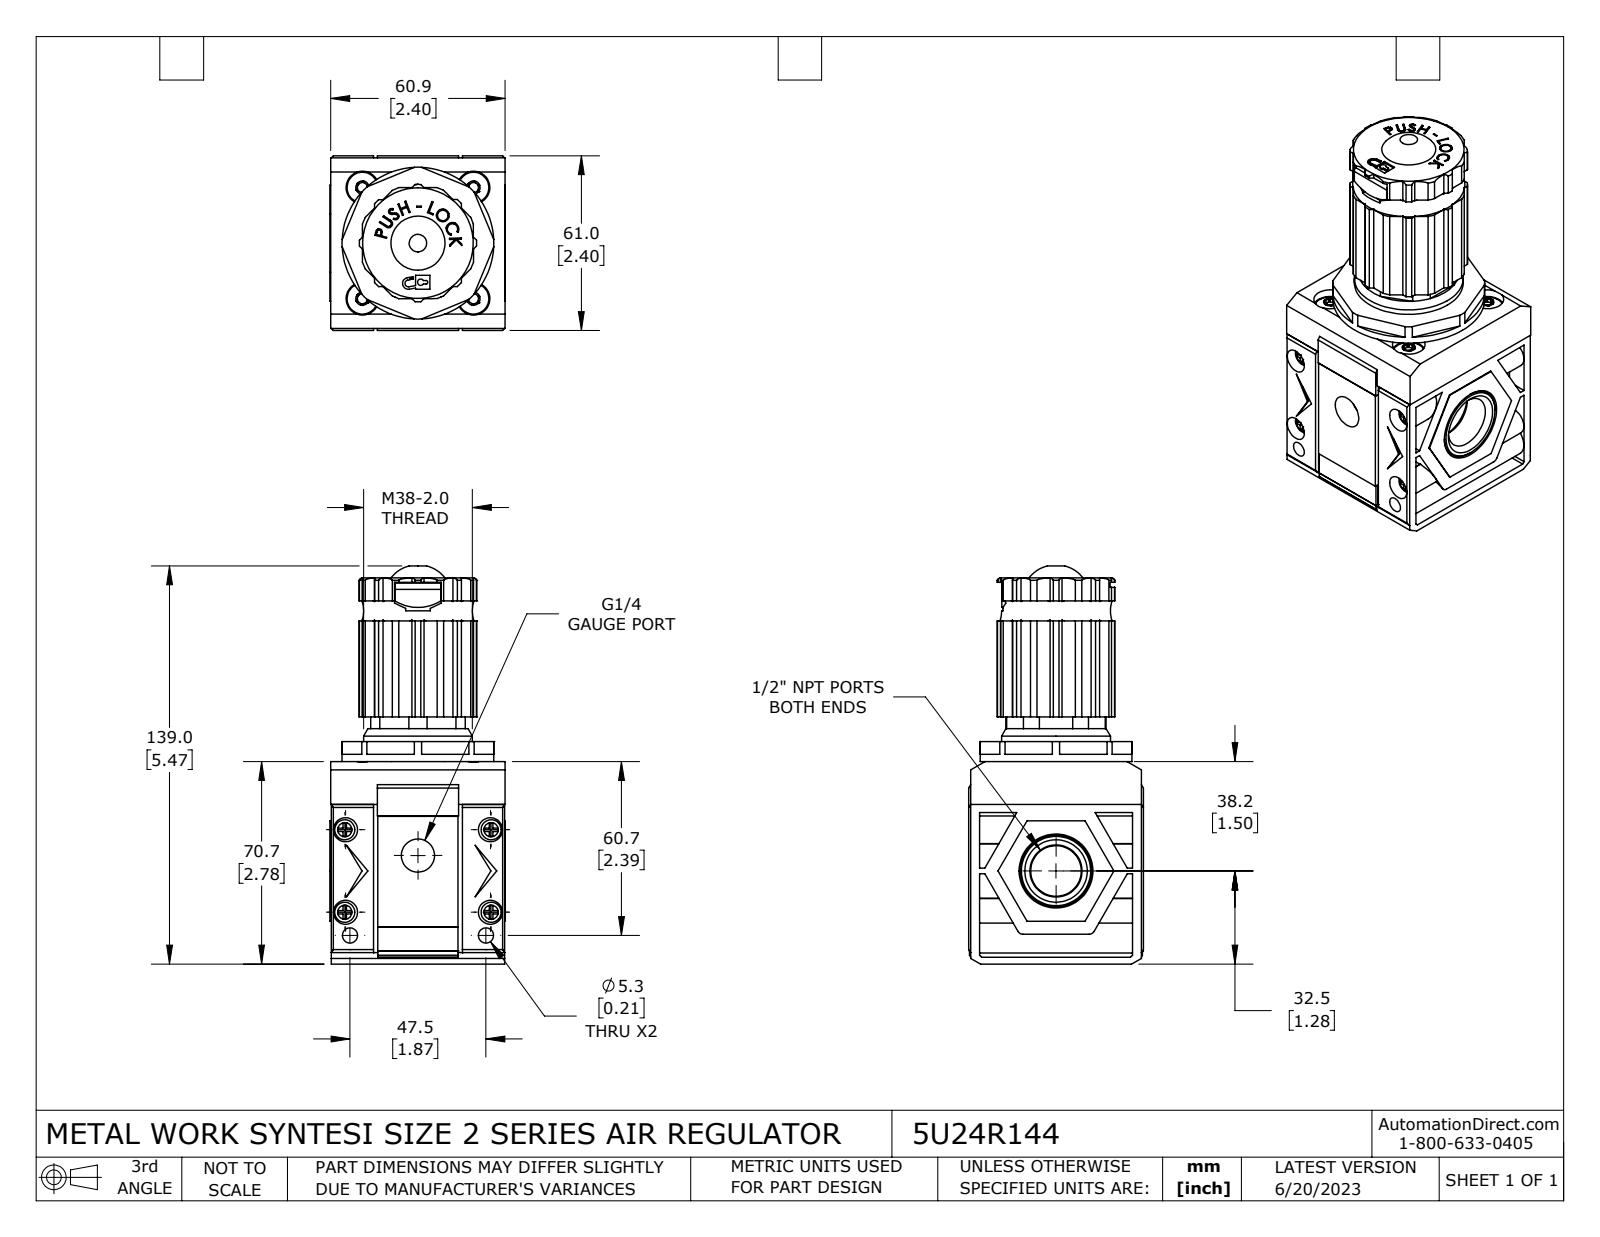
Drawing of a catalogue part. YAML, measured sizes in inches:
part_name: "5U24R144"
step_written_by: "SolidWorks 2021 (CONFIG_CONTROL_DESIGN)"
units: inches
bodies: {solids: 13, faces: 1071, planar: 610, cylindrical: 329, other: 132}
overall_size: [5.472, 2.411, 2.402]
volume: 16.93
surface_area: 128.7
round_holes:
  - {diameter: 0.128, count: 4}
  - {diameter: 0.165, count: 4}
  - {diameter: 0.331, count: 4}
  - {diameter: 0.449, count: 4}
  - {diameter: 0.209, count: 2}
  - {diameter: 0.457, count: 1}
  - {diameter: 1.25, count: 1}
  - {diameter: 1.411, count: 1}
  - {diameter: 1.508, count: 1}
round_bosses_or_shafts:
  - {diameter: 0.276, count: 4}
  - {diameter: 0.189, count: 4}
  - {diameter: 0.15, count: 4}
  - {diameter: 2.087, count: 1}
  - {diameter: 1.496, count: 1}
  - {diameter: 1.248, count: 1}
  - {diameter: 1.035, count: 1}
  - {diameter: 0.925, count: 1}
partial_cylinders:
  - {radius: 0.011, count: 28}
  - {radius: 0.069, count: 4}
  - {radius: 0.191, count: 4}
  - {radius: 0.807, count: 4}
  - {radius: 0.079, count: 2}
  - {radius: 0.242, count: 2}
  - {radius: 0.022, count: 1}
  - {radius: 0.025, count: 1}
face_to_face_distances: [2.39, 0.094, 2.193, 2.098, 2.402, 0.591, 2.319, 2.783, 2.689, 1.559]
hole_center_spacings: [1.08, 1.528, 0.325, 1.057, 1.134, 1.265, 1.443, 1.454]
